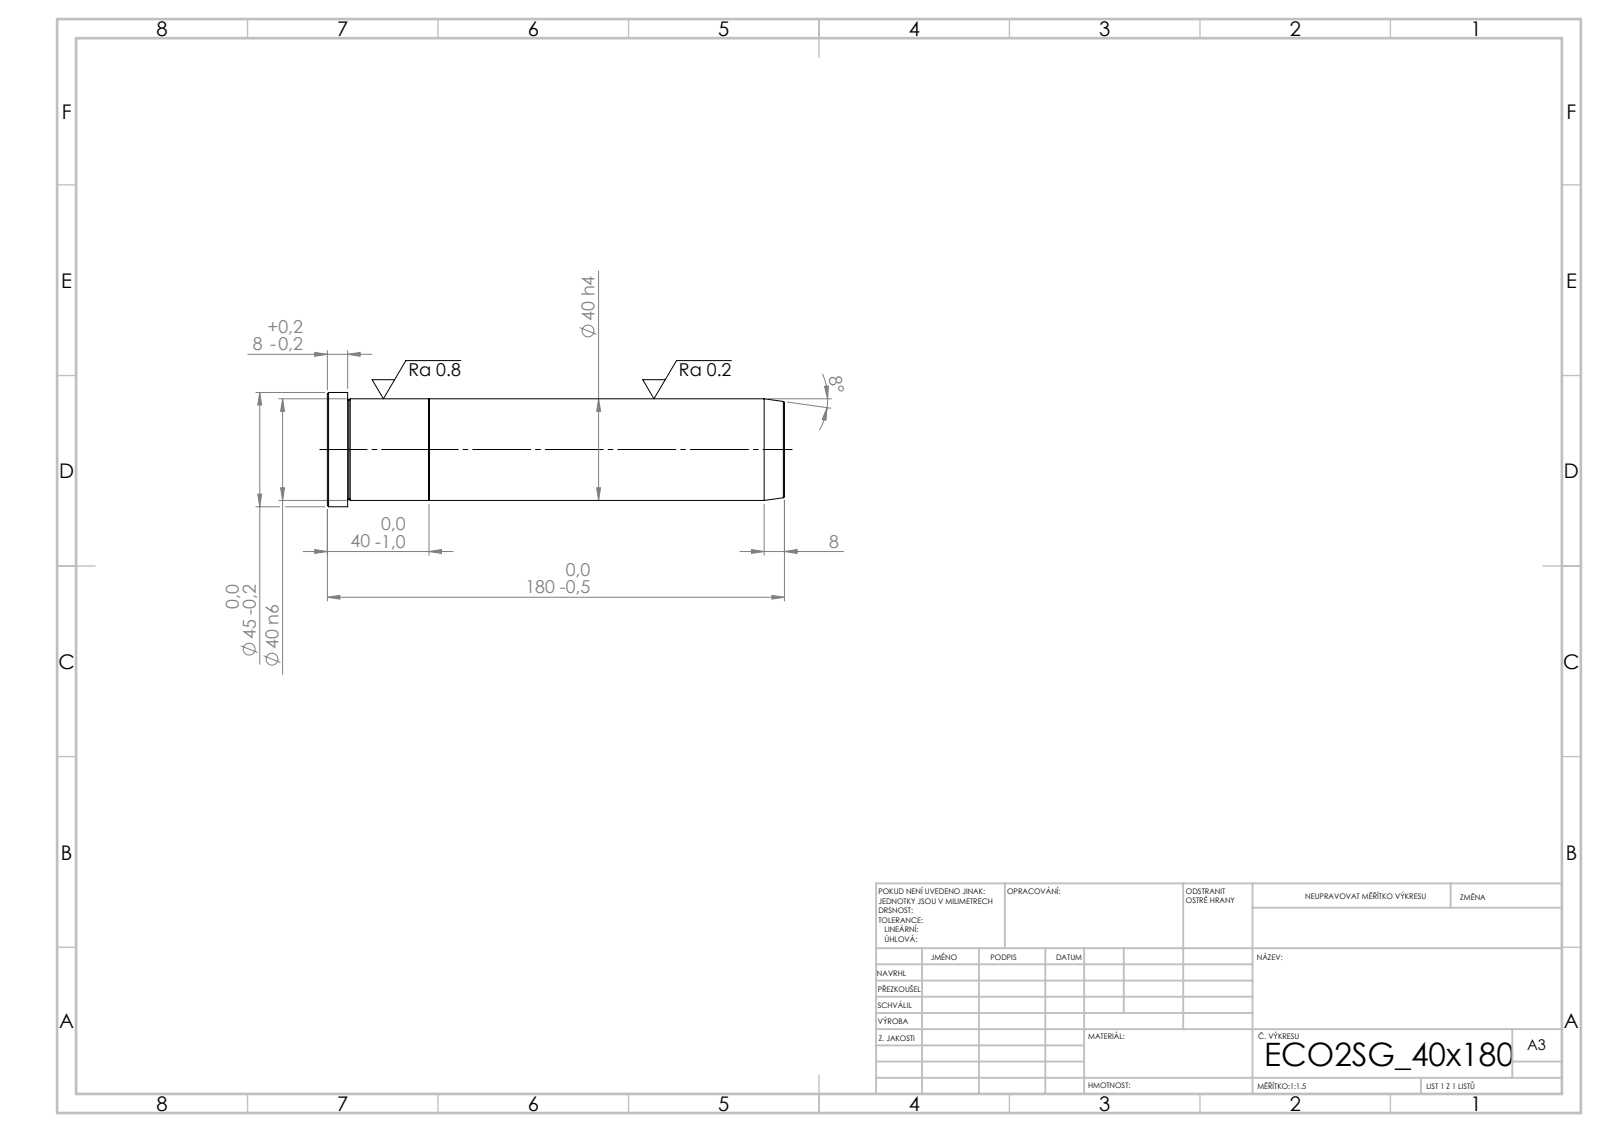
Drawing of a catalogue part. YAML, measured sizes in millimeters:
step_written_by: "SolidWorks 2019 (CONFIG_CONTROL_DESIGN)"
units: millimeters
bodies: {solids: 2, faces: 21, planar: 5, cylindrical: 6, other: 10}
overall_size: [180, 45, 45]
volume: 228240
surface_area: 28292
round_bosses_or_shafts:
  - {diameter: 45, count: 1}
  - {diameter: 40, count: 1}
face_to_face_distances: [40, 140, 180, 172, 32, 8]
